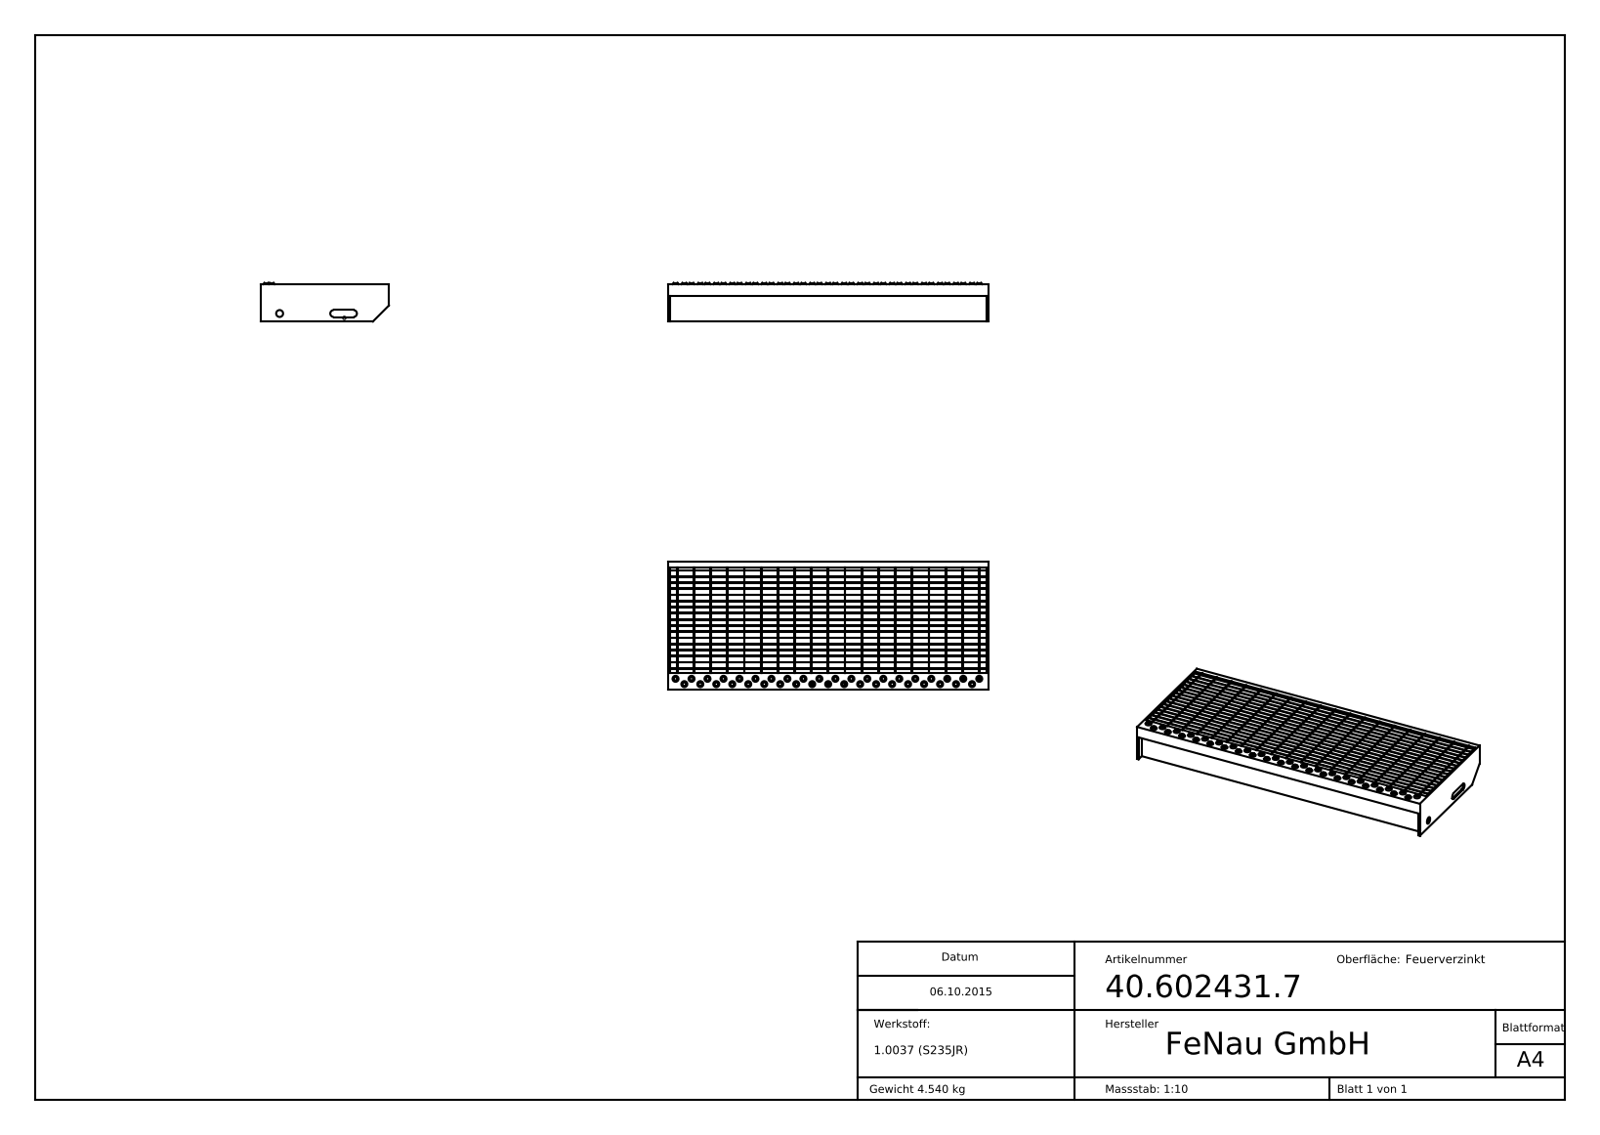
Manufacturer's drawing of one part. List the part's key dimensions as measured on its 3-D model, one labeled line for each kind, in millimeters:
Part name (STEP PRODUCT): 40.602431.7
STEP written by: SolidWorks 2015 (CONFIG_CONTROL_DESIGN)
Units: millimetres
Bodies: 28 solids, 731 faces (485 planar, 88 cylindrical, 158 other)
Overall size (bounding box): 600 × 240 × 72.67
Volume: 582 114 mm³ · Surface area: 689 029 mm²
Round holes (diameter × count): ⌀7 ×39, ⌀13 ×1
Partial cylindrical surfaces — rounded edges, fillets, slot ends (radius × count): R6.5 ×2
Main face-to-face distances: 2, 1.5, 31.5, 13, 11.5, 33, 23, 63, 20, 216.5
Hole centre spacings: 30, 60, 90, 120, 150, 180, 210, 240
